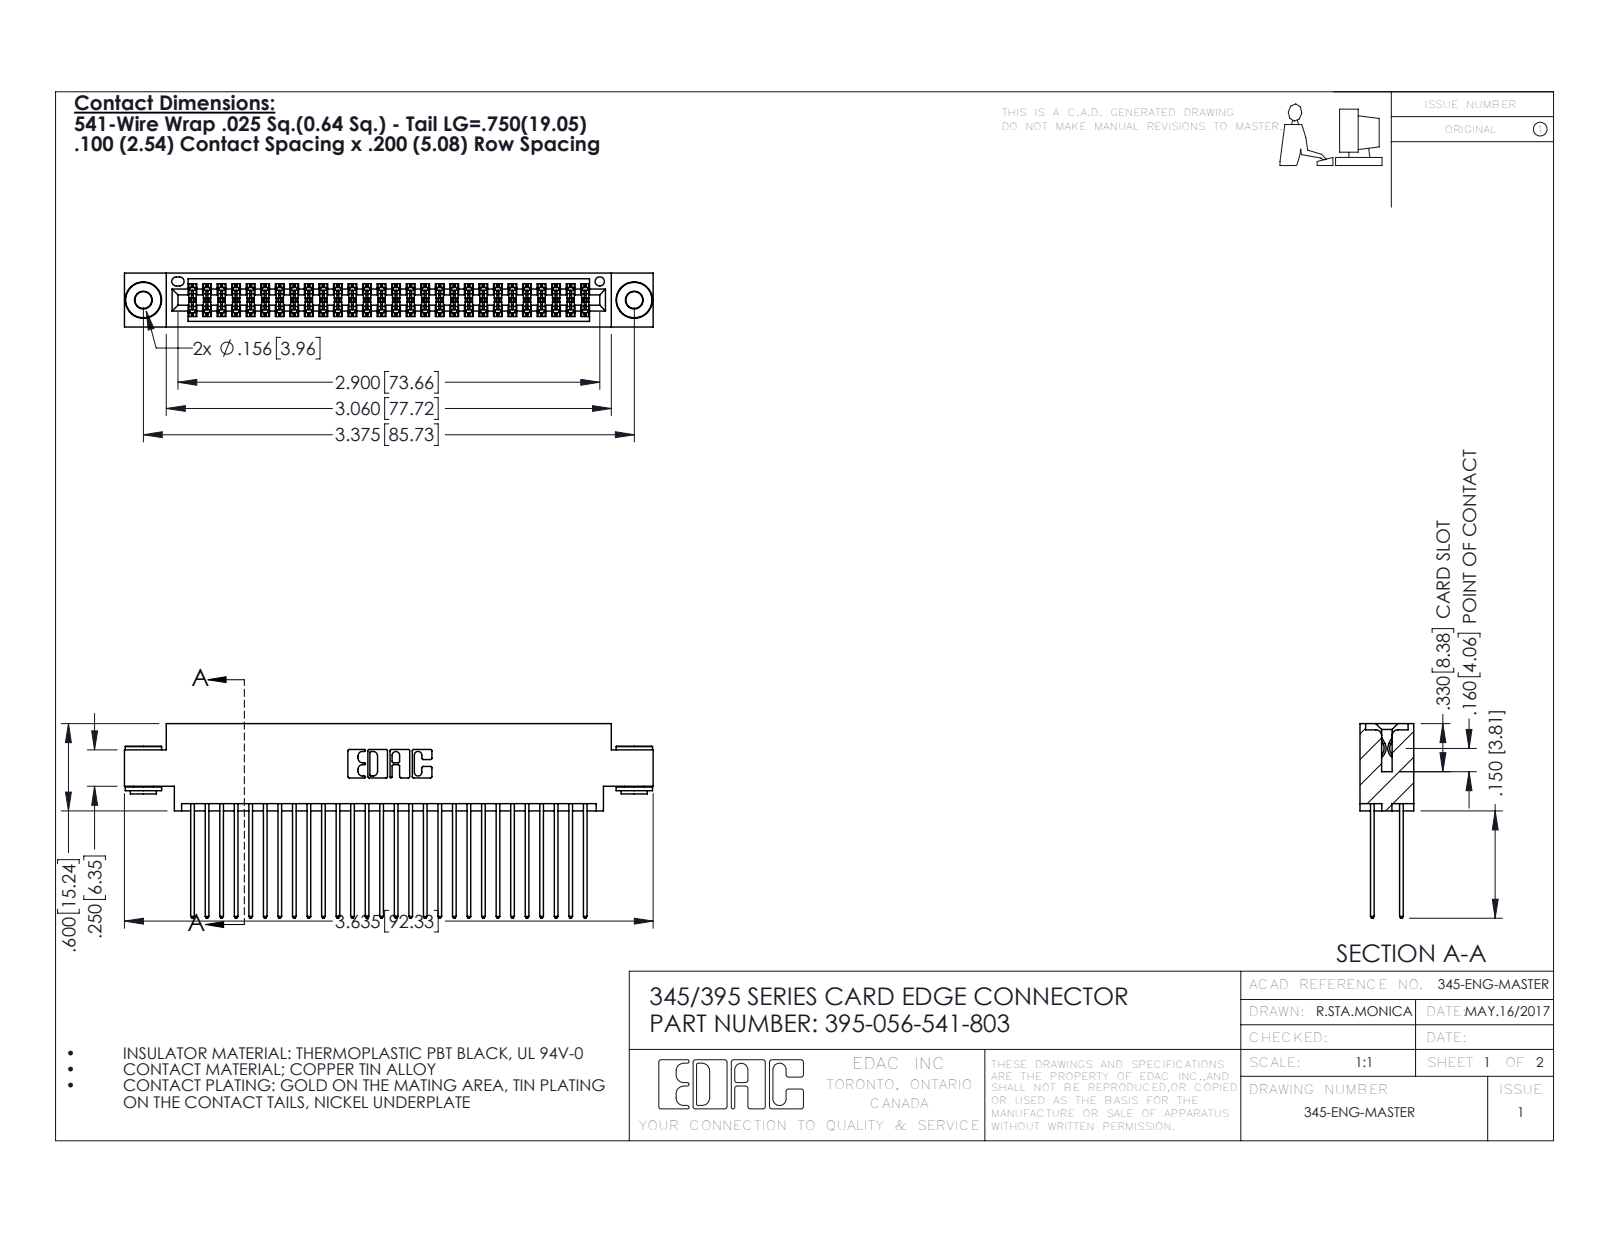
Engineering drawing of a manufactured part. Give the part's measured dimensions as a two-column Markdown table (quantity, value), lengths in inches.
| quantity | value |
| --- | --- |
| part name | 345 Part_0.170 Offset - 0.156 Dia-TH; 345-250-002_345-250-002-102; 345-292-001_345-293-141; 395-056-541-803 |
| STEP written by | SolidWorks 2016 (CONFIG_CONTROL_DESIGN) |
| units | inches |
| bodies | 59 solids, 2968 faces (1942 planar, 1018 cylindrical, 8 other) |
| overall size | 3.635 × 1.337 × 0.37 |
| volume | 0.553 in³ |
| surface area | 23.23 in² |
| round holes (diameter × count) | 0.116 × 2, 0.156 × 2, 0.064 × 1 |
| round bosses / shafts (diameter × count) | 0.25 × 2, 0.18 × 2, 0.136 × 2 |
| partial cylindrical surfaces (radius × count) | 0.006 × 84, 0.01 × 56, 0.01 × 22, 0.007 × 6, 0.031 × 6, 0.026 × 3, 0.014 × 2, 0.019 × 2 |
| main face-to-face distances | 0.072, 0.298, 0.2, 0.098, 0.272, 0.025, 0.37, 0.225, 0.175, 0.149 |
| hole center spacings | 0.27, 3.14, 3.375 |
